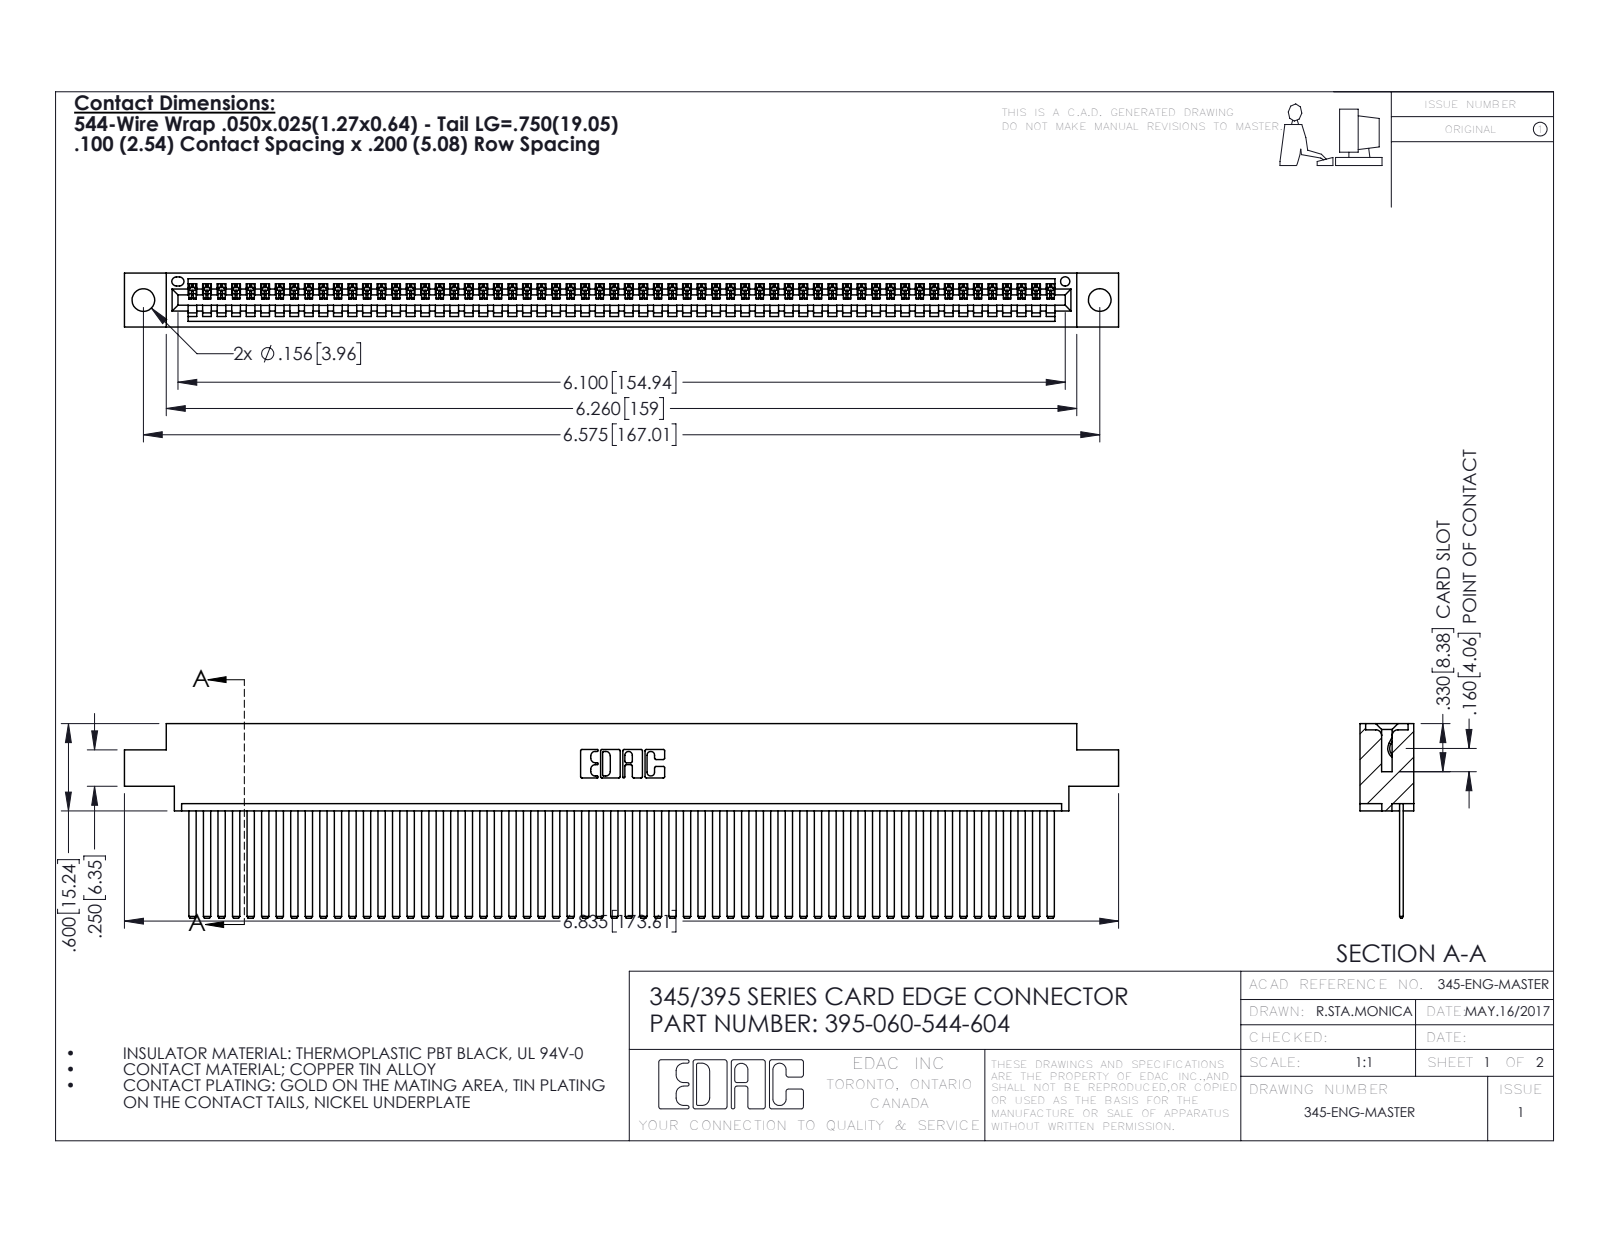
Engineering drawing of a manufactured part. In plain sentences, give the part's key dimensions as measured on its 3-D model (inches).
The part is named "345-292-001_345-293-144; 345 Part_0.170 Offset - 0.156 Dia-TH; 395-060-544-604". Its 3-D file was written by "SolidWorks 2016 (CONFIG_CONTROL_DESIGN)". It is 61 solids with 3250 faces: 2244 planar, 1006 cylindrical and 0 other. Overall it measures 6.835 by 1.337 by 0.37 inches. Its volume is 1.045 cubic inches and its surface area 38.8 square inches. Round holes: 2 of diameter 0.156, 1 of diameter 0.064. Partial cylindrical surfaces (rounded edges, fillets, slot ends): 120 of radius 0.006, 22 of radius 0.01, 6 of radius 0.007, 6 of radius 0.031, 3 of radius 0.026, 2 of radius 0.031, 2 of radius 0.04, 1 of radius 0.014. The main face-to-face distances are 0.072, 0.298, 0.025, 0.098, 0.272, 0.37, 0.2, 0.225, 0.175, 0.149. The hole center spacings are 0.27, 6.339, 6.575.
